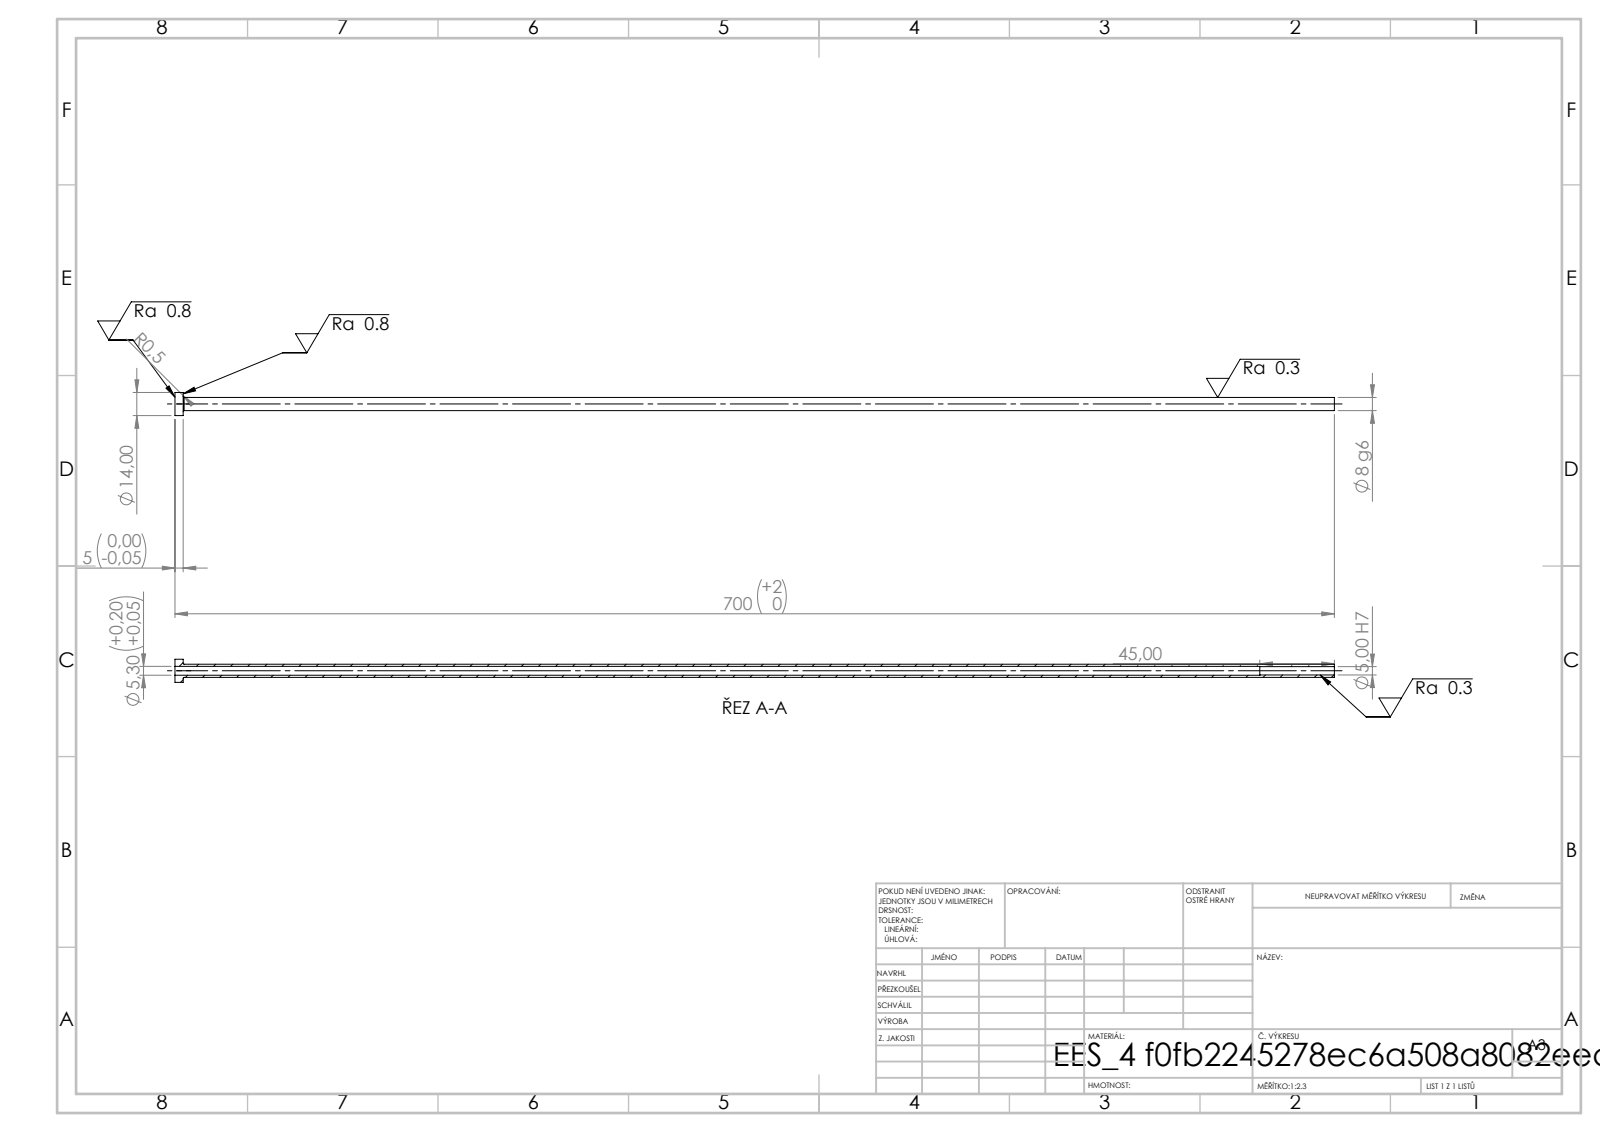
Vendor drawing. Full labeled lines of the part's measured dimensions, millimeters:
STEP written by: SolidWorks 2019 (CONFIG_CONTROL_DESIGN)
Units: millimetres
Bodies: 1 solid, 14 faces (4 planar, 8 cylindrical, 2 other)
Overall size (bounding box): 700 × 14 × 14
Volume: 20 372 mm³ · Surface area: 29 563 mm²
Round holes (diameter × count): ⌀5 ×1, ⌀5.3 ×1
Round bosses / shafts (diameter × count): ⌀14 ×1, ⌀8 ×1
Main face-to-face distances: 5, 700, 695, 655, 650, 45
